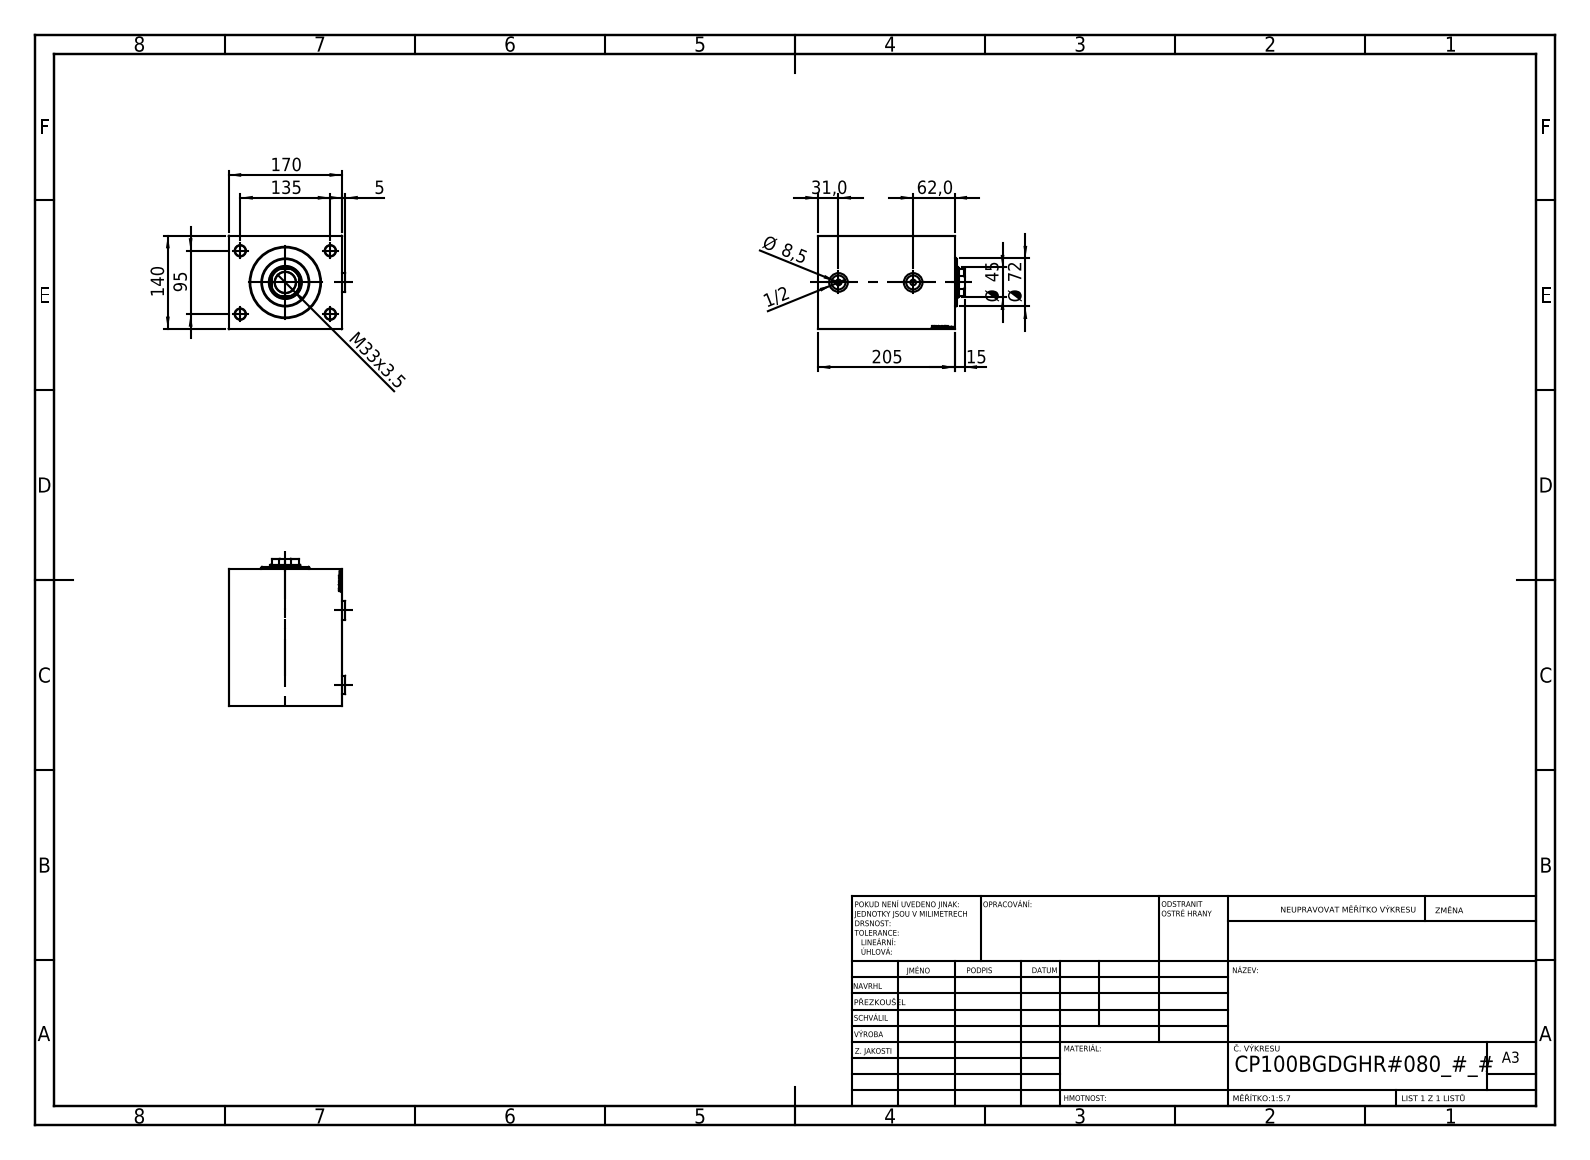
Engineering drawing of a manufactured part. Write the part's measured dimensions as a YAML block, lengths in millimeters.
part_name: "V450CP_B; V450CP_B_VCP; V450CP_VC_B; PLUG"
step_written_by: "SolidWorks 2019 (CONFIG_CONTROL_DESIGN)"
units: millimeters
bodies: {solids: 5, faces: 958, planar: 440, cylindrical: 84, other: 434}
overall_size: [220, 174.9, 140]
volume: 4305000
surface_area: 351825
round_holes:
  - {diameter: 16, count: 4}
  - {diameter: 4, count: 2}
  - {diameter: 8.5, count: 2}
  - {diameter: 9.73, count: 2}
  - {diameter: 15, count: 2}
  - {diameter: 20.96, count: 2}
  - {diameter: 28, count: 2}
  - {diameter: 31.5, count: 1}
  - {diameter: 45, count: 1}
  - {diameter: 48.5, count: 1}
  - {diameter: 49.5, count: 1}
  - {diameter: 100, count: 1}
round_bosses_or_shafts:
  - {diameter: 72, count: 1}
partial_cylinders:
  - {radius: 22, count: 1}
face_to_face_distances: [140, 170, 205, 26, 179, 136, 110, 69, 56, 30]
hole_center_spacings: [82.54, 95, 135, 165.08, 43.19, 112]
